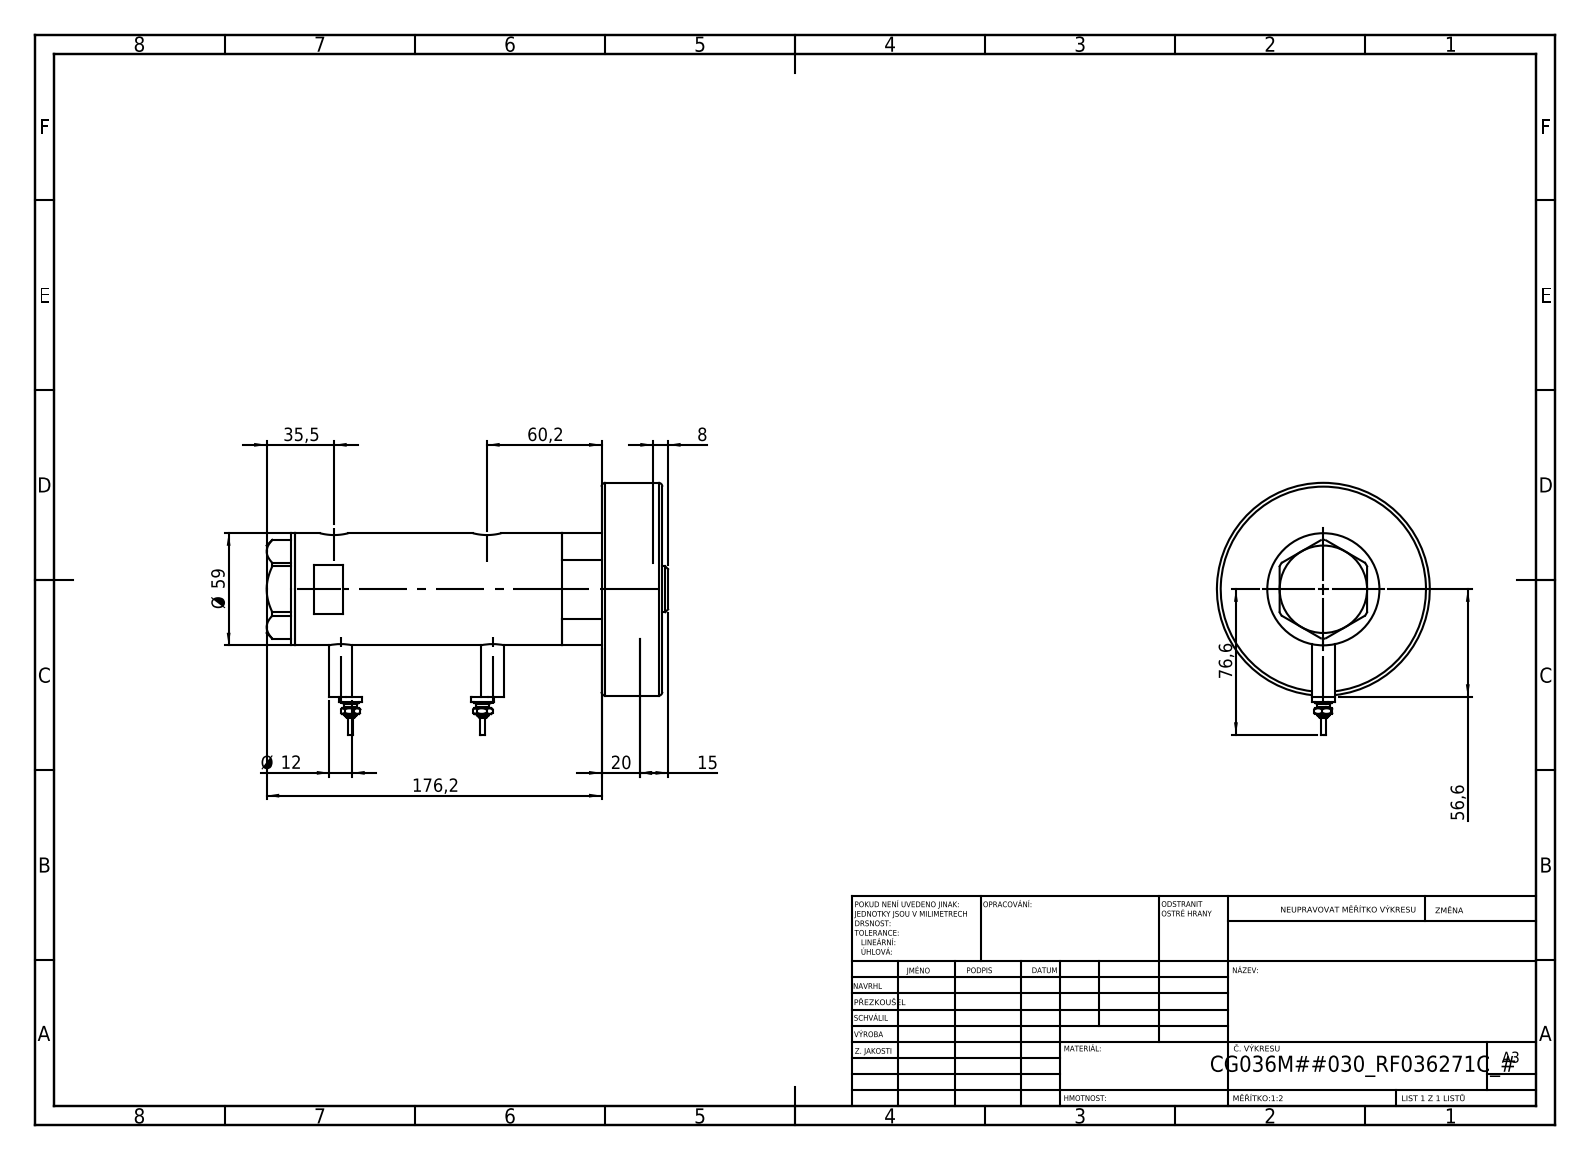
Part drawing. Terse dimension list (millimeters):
name: V270CG_FRONT; V270CG_MIDDLE; V270CG_271C; V270CG_BACK (+2 more)
written by: SolidWorks 2019 (CONFIG_CONTROL_DESIGN)
unit: mm
bodies: 7 solids, 222 faces (81 planar, 73 cylindrical, 68 other)
size: 211.2 × 132.6 × 112
volume: 751 758 mm³; area: 135 007 mm²
holes: 2× ⌀9.73, 2× ⌀12.5, 2× ⌀15, 1× ⌀8.5, 1× ⌀25, 1× ⌀26.5, 1× ⌀36, 1× ⌀40, 1× ⌀48, 1× ⌀52
bosses: 4× ⌀12, 2× ⌀9, 2× ⌀7, 2× ⌀4.5, 2× ⌀2.5, 1× ⌀112, 1× ⌀59, 1× ⌀46
face distances: 32, 161.2, 193.2, 102.2, 59, 91, 23.5, 78.7, 137.7, 169.7
hole spacings: 2.9, 3.5, 77, 79.9, 80.5, 83.4
